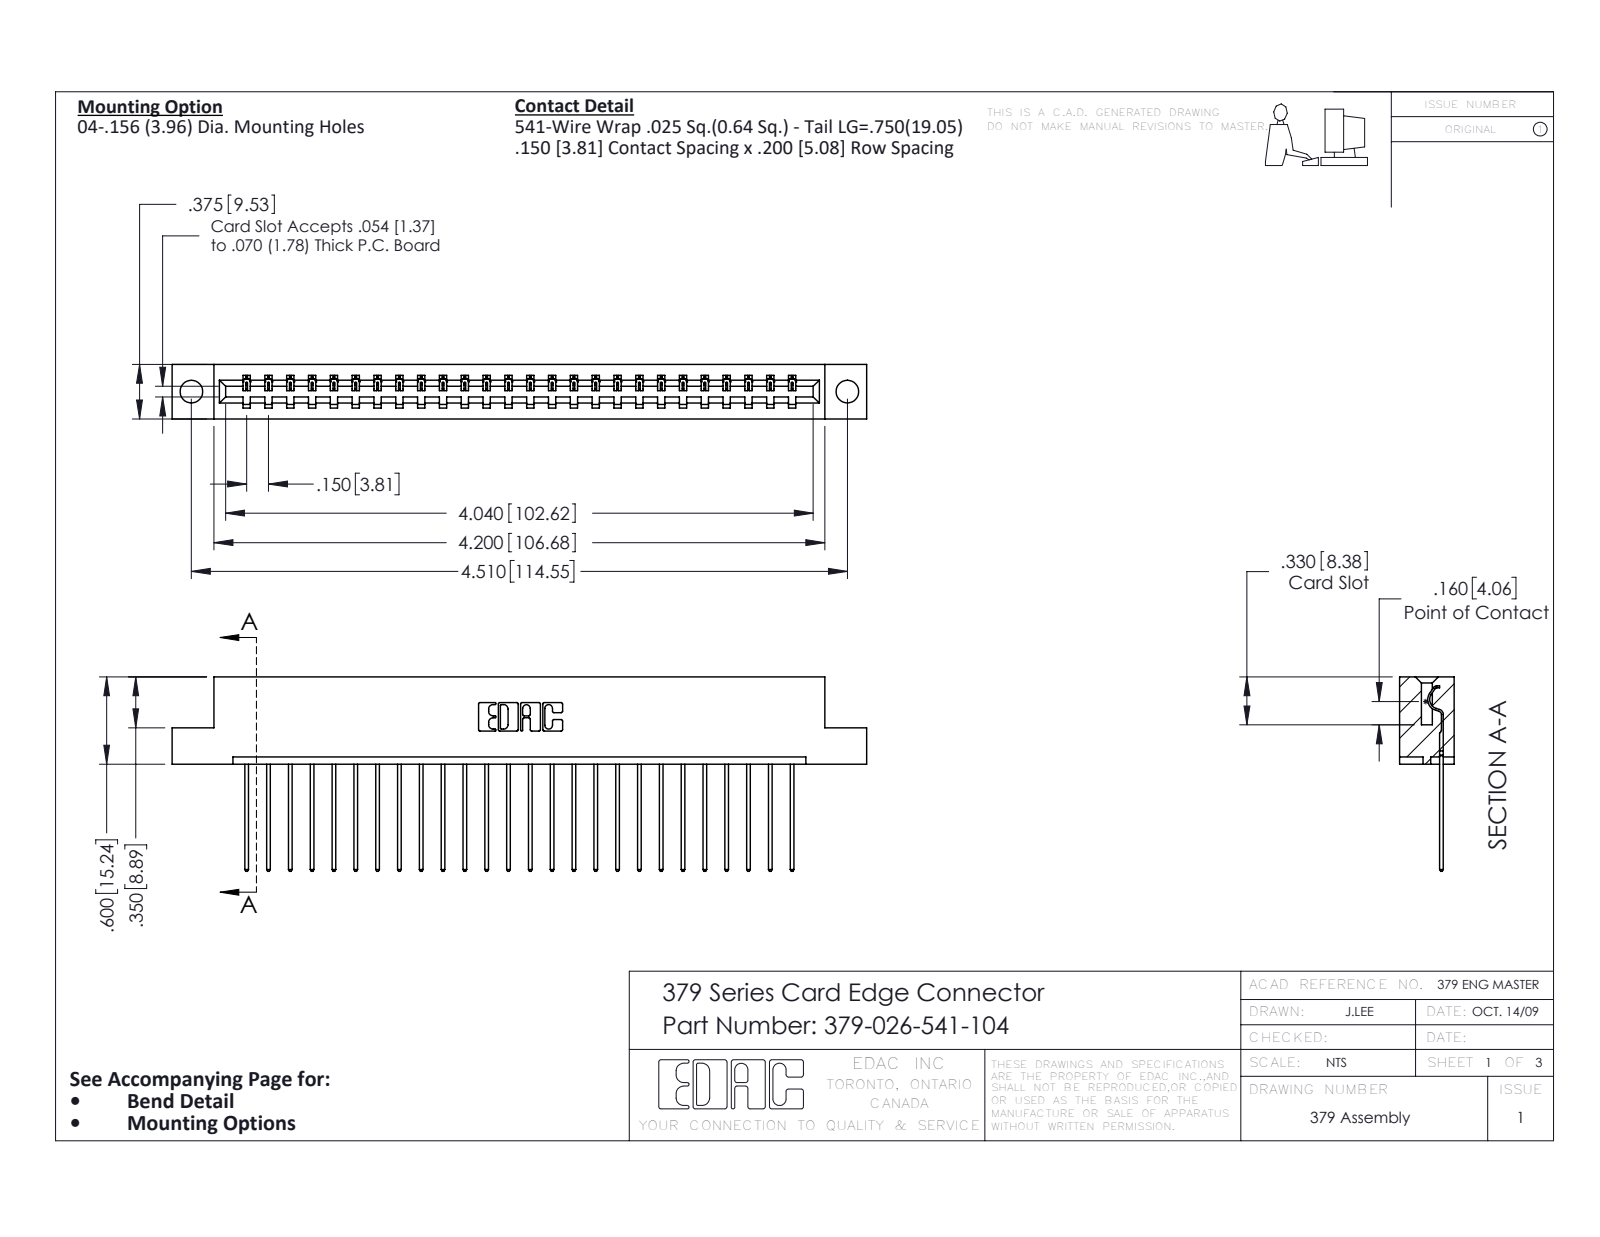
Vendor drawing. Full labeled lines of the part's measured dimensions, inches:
Part name (STEP PRODUCT): 379 Part_Flush - .156 Dia - TH; 379-026-541-104; 345-292-001_345-293-141
STEP written by: SolidWorks 2016 (CONFIG_CONTROL_DESIGN)
Units: inches
Bodies: 27 solids, 1622 faces (1162 planar, 460 cylindrical, 0 other)
Overall size (bounding box): 4.775 × 1.337 × 0.375
Volume: 0.766 in³ · Surface area: 20.28 in²
Round holes (diameter × count): ⌀0.156 ×2
Partial cylindrical surfaces — rounded edges, fillets, slot ends (radius × count): R0.006 ×52, R0.01 ×52, R0.01 ×22, R0.007 ×6, R0.031 ×6, R0.026 ×3, R0.014 ×1, R0.022 ×1
Main face-to-face distances: 0.3, 0.075, 0.375, 0.225, 0.6, 0.275, 0.1, 0.025, 0.2, 0.15
Hole centre spacings: 4.51
